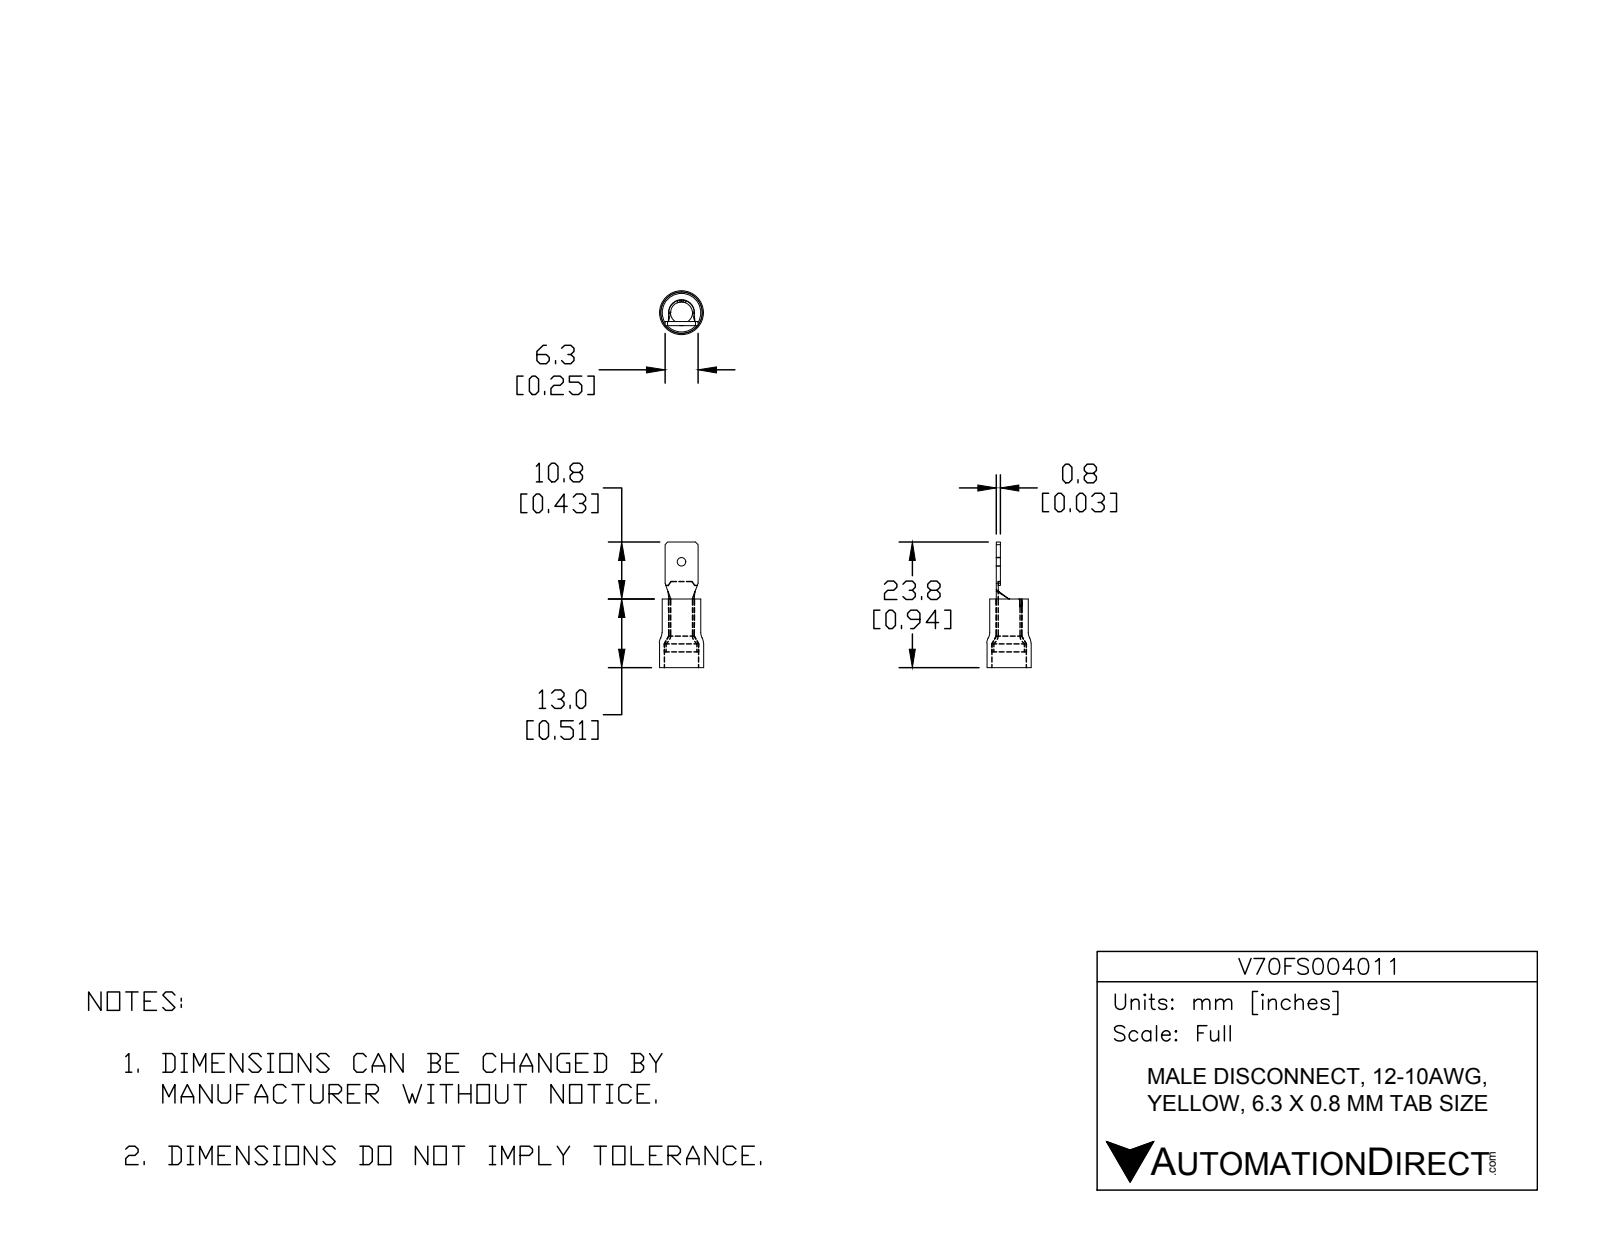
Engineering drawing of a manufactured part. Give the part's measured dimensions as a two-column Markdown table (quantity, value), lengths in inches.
| quantity | value |
| --- | --- |
| part name | V70FS004011 |
| STEP written by | SolidWorks 2017 (AUTOMOTIVE_DESIGN) |
| units | inches |
| bodies | 2 solids, 66 faces (22 planar, 20 cylindrical, 24 other) |
| overall size | 0.937 × 0.329 × 0.329 |
| volume | 0.024 in³ |
| surface area | 1.654 in² |
| round holes (diameter × count) | 0.063 × 1, 0.163 × 1, 0.228 × 1, 0.256 × 1 |
| round bosses / shafts (diameter × count) | 0.329 × 1, 0.287 × 1, 0.19 × 1 |
| partial cylindrical surfaces (radius × count) | 0.02 × 4 |
| main face-to-face distances | 0.03, 0.512, 0.016, 0.014, 0.118, 0.394, 0.246, 0.937, 0.819, 0.425 |
